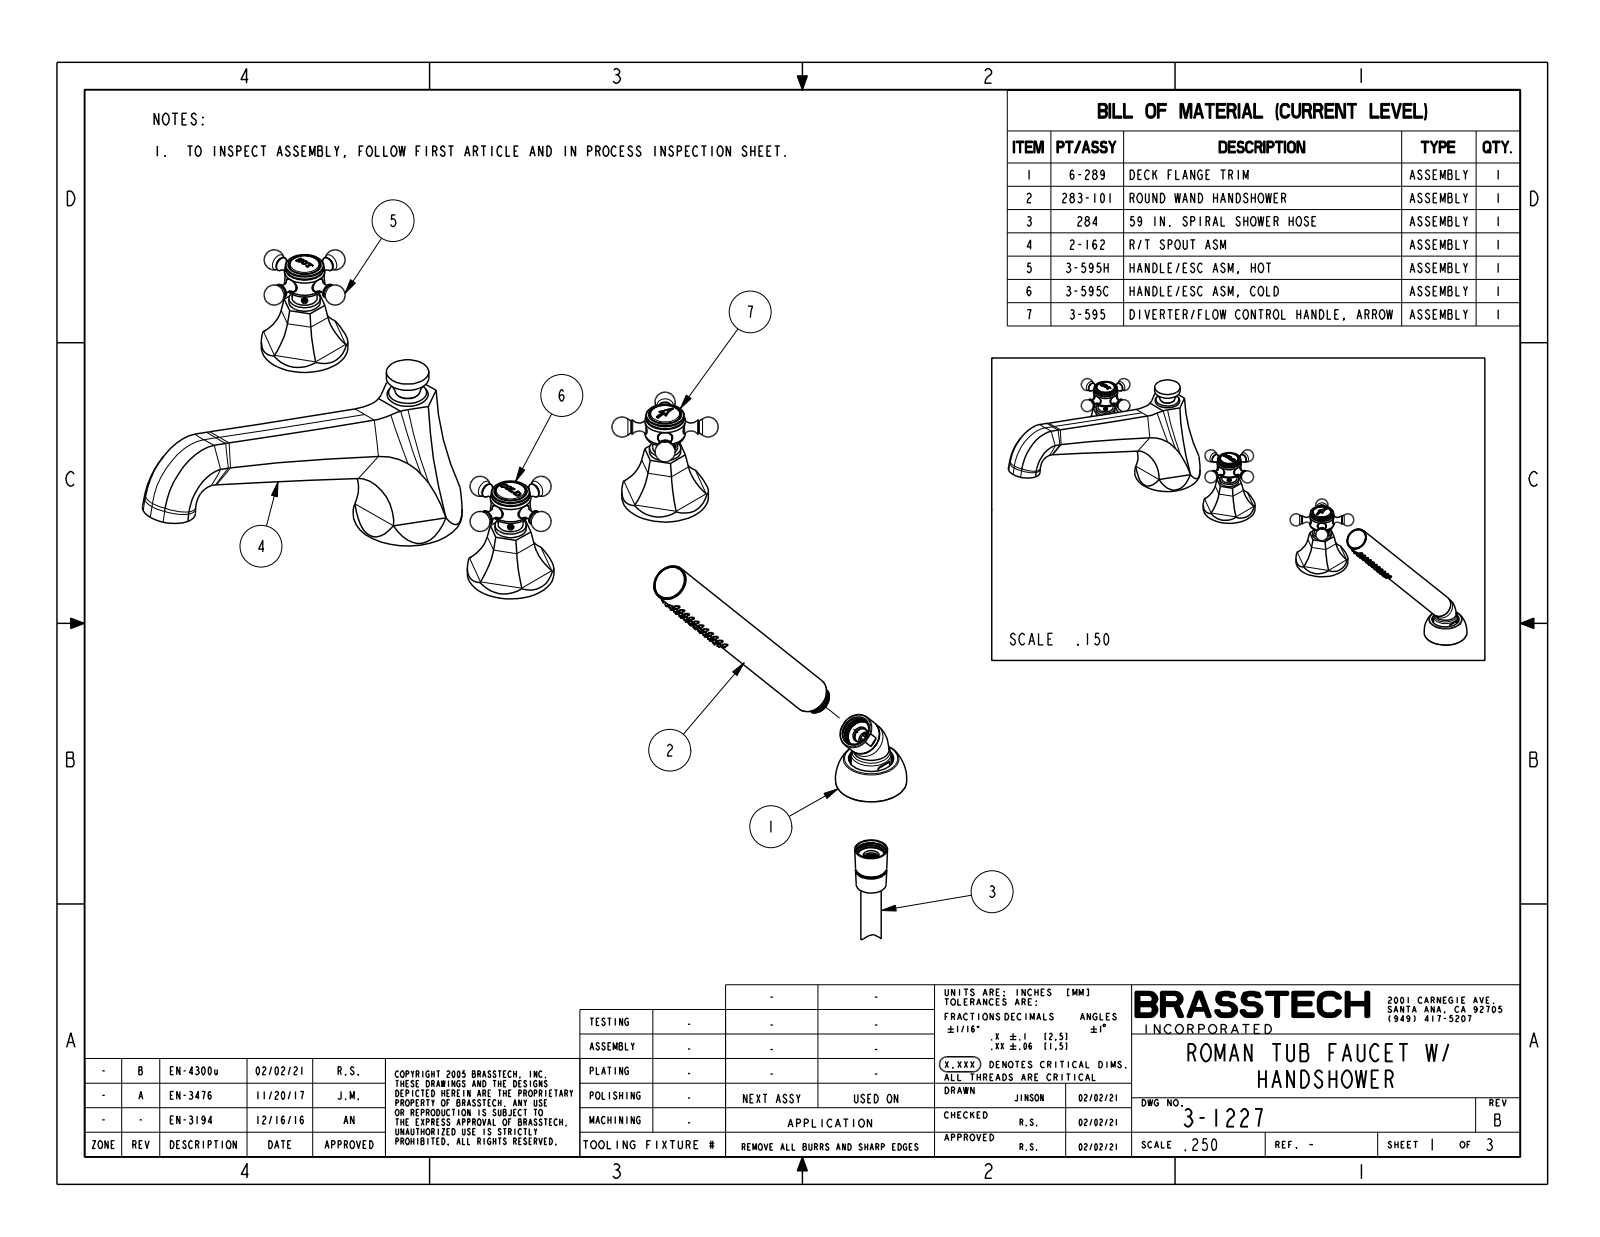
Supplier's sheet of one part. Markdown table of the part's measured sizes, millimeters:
| quantity | value |
| --- | --- |
| part name | 3-1227 |
| STEP written by | CREO PARAMETRIC BY PTC INC, 2018400 (CONFIG_CONTROL_DESIGN) |
| units | millimeters |
| bodies | 7 solids, 1426 faces (167 planar, 393 cylindrical, 866 other) |
| overall size | 620.7 × 291.7 × 224.8 |
| volume | 939 100 mm³ |
| surface area | 134 400 mm² |
| round holes (diameter × count) | 3.6 × 44, 10.4 × 5, 21.7 × 3, 3.8 × 1 |
| round bosses / shafts (diameter × count) | 10 × 5, 60.3 × 3, 26.8 × 3, 21.8 × 3, 17.4 × 3, 10.2 × 3, 75.9 × 1, 29.5 × 1 |
| partial cylindrical surfaces (radius × count) | 39.1 × 18, 0.2 × 7, 0.6 × 7, 1.3 × 6, 330.2 × 6, 0.8 × 5, 1.2 × 3, 0.4 × 2 |
| main face-to-face distances | 41.8, 99.8, 74.8, 174.6, 38.8, 3, 0.5, 104.5, 65.7, 62.7 |
| hole center spacings | 8.5, 4.3, 11.4, 17.1, 15.3, 7.4, 22.1, 22.5 |
